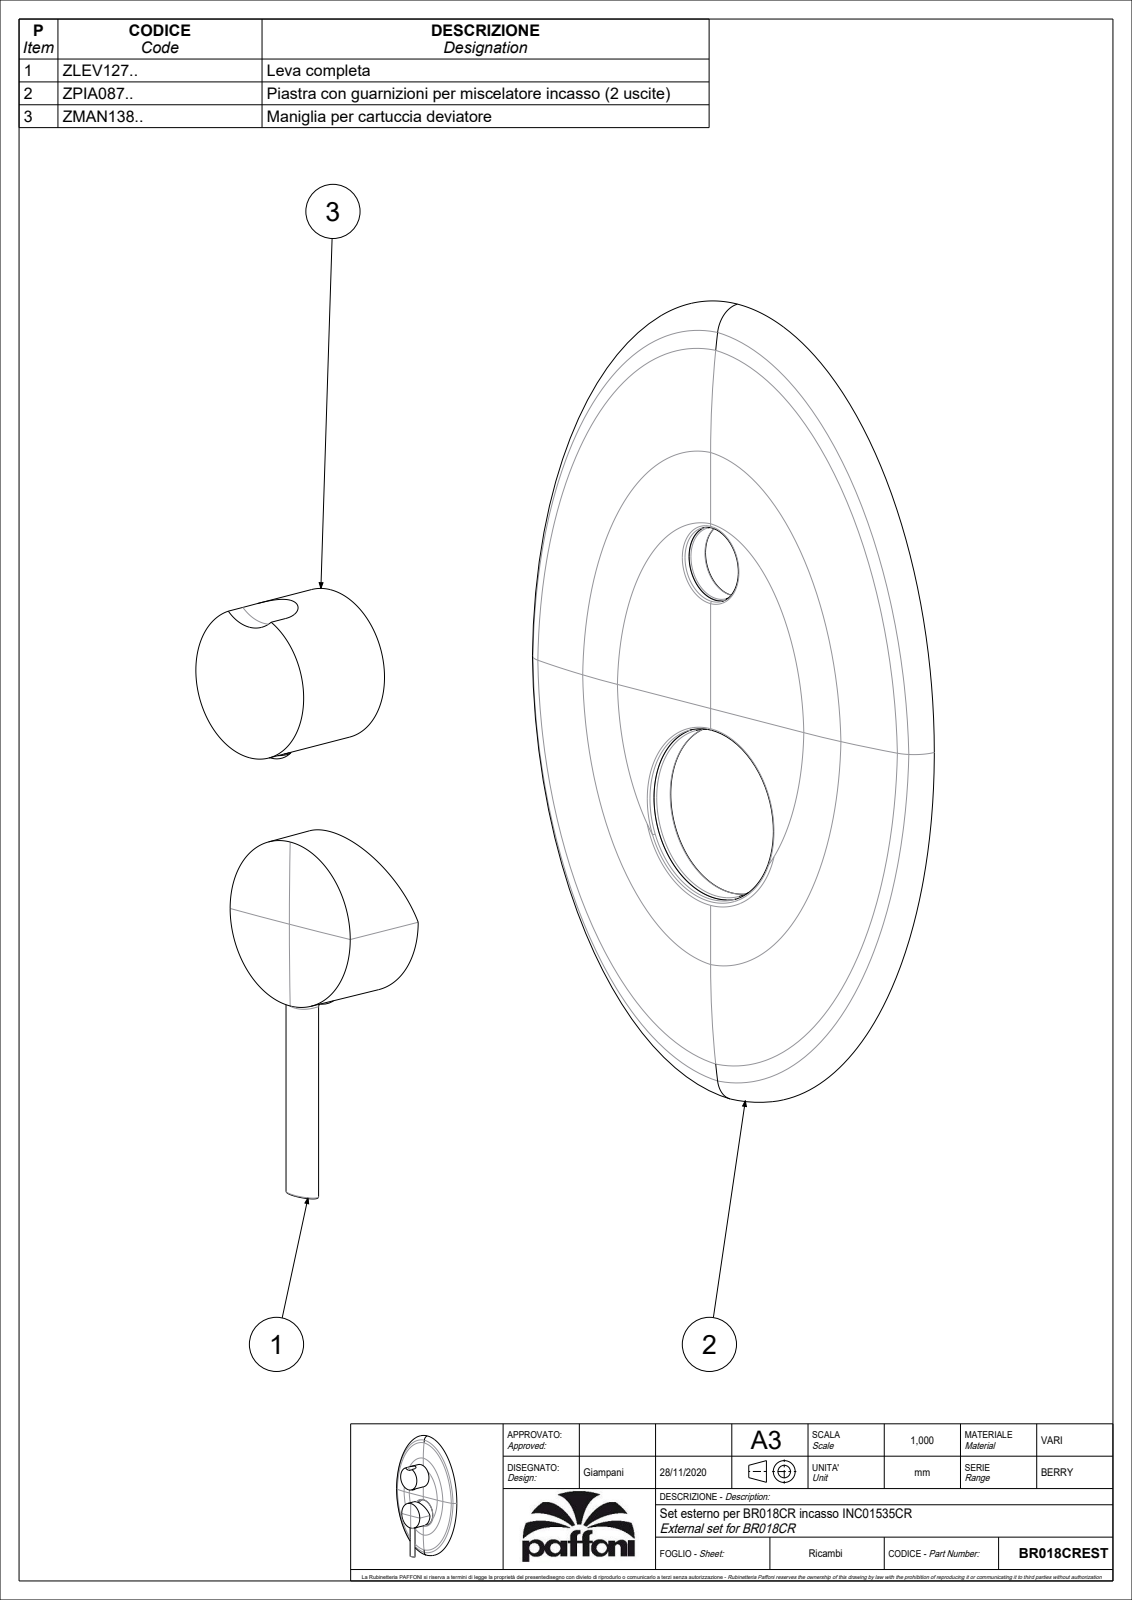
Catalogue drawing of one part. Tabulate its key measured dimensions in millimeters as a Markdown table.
| quantity | value |
| --- | --- |
| part name | BR018CREST |
| STEP written by | CREO PARAMETRIC BY PTC INC, 2020044 (CONFIG_CONTROL_DESIGN) |
| units | millimeters |
| bodies | 3 solids, 284 faces (84 planar, 81 cylindrical, 119 other) |
| overall size | 216 × 146 × 46.68 |
| volume | 96 586 mm³ |
| surface area | 74 609 mm² |
| round holes (diameter × count) | 3 × 2, 3.2 × 1, 3.5 × 1, 4.2 × 1, 7.8 × 1, 14.8 × 1, 19.2 × 1, 20 × 1, 21 × 1, 23.2 × 1, 36 × 1, 45 × 1 |
| round bosses / shafts (diameter × count) | 7.6 × 2, 5.5 × 2, 51 × 1, 49 × 1, 40 × 1, 25 × 1, 24 × 1, 23 × 1 |
| partial cylindrical surfaces (radius × count) | 1.25 × 4, 0.8 × 2, 1 × 2, 1.9 × 1, 2.5 × 1, 12.5 × 1 |
| main face-to-face distances | 39, 9, 2, 14, 30, 37, 28, 16, 23, 18 |
| hole center spacings | 0.5, 6.5, 7, 10, 68, 78 |
